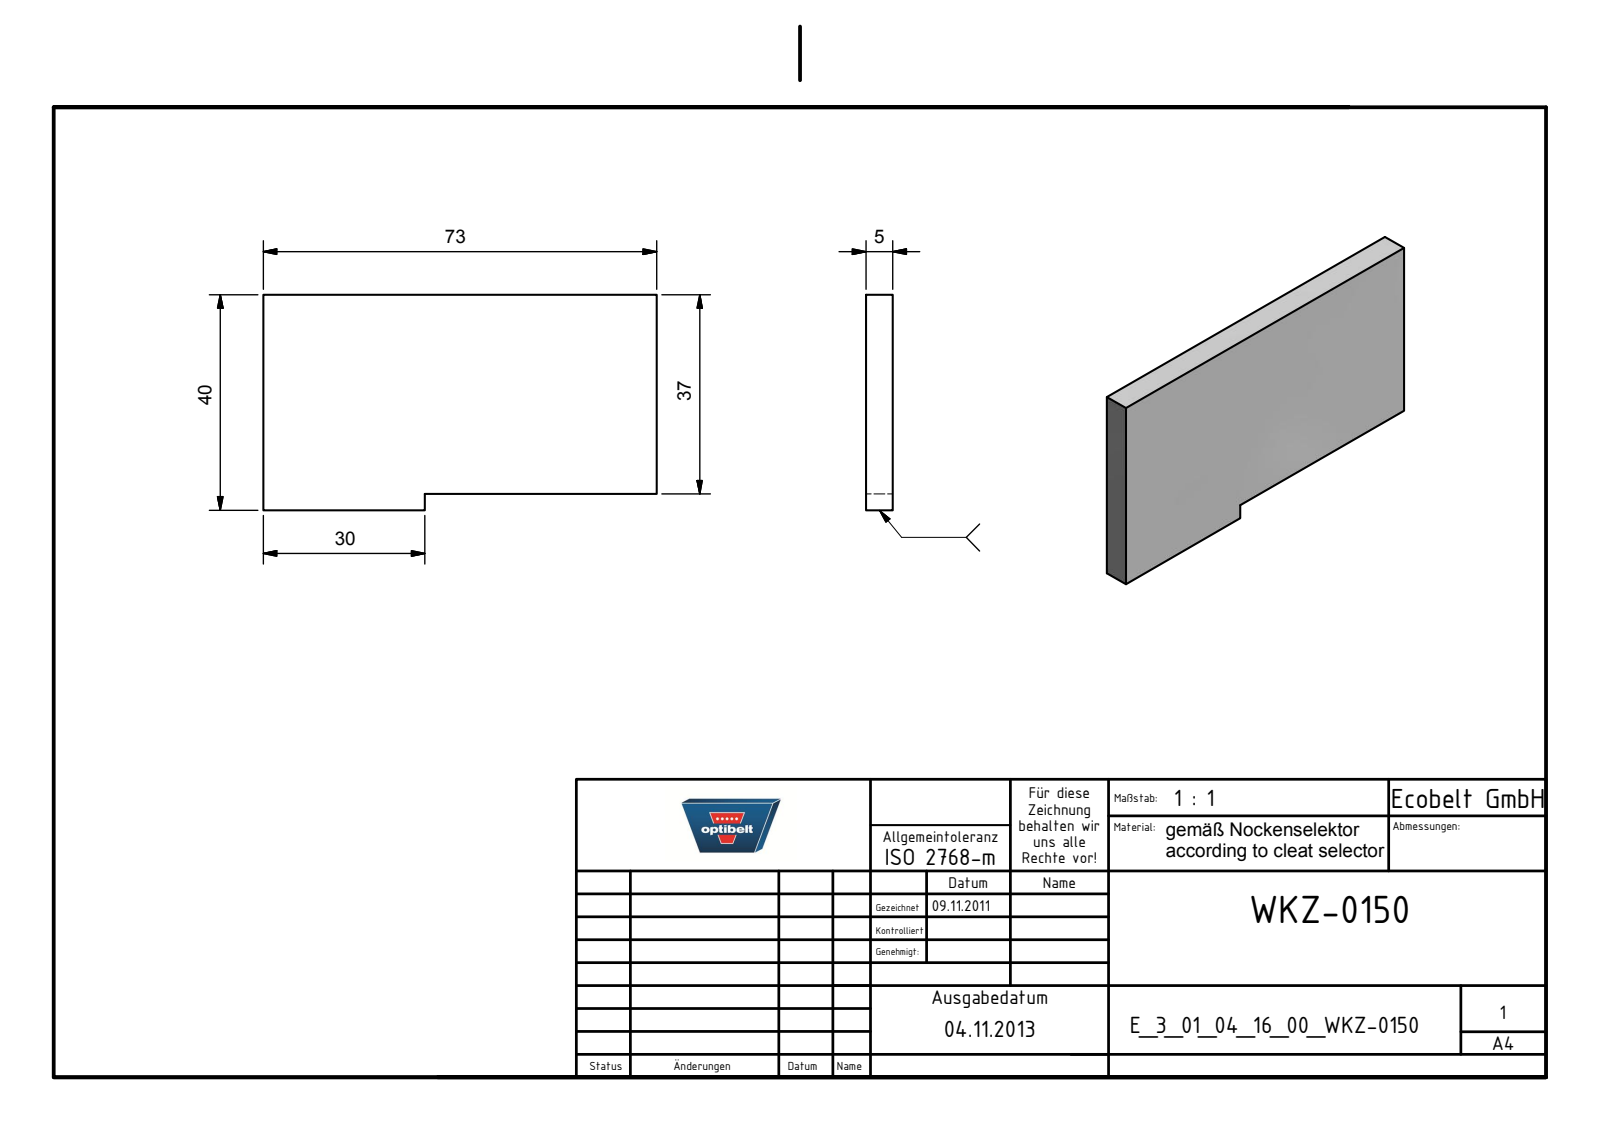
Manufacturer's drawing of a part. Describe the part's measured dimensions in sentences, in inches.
The part is named "E_3_01_04_16_00_WKZ-0150". Its 3-D file was written by "Autodesk Inventor 2025 (AUTOMOTIVE_DESIGN)". It is 1 solid with 8 faces: 8 planar, 0 cylindrical and 0 other. Overall it measures 2.874 by 1.575 by 0.197 inches. Its volume is 0.852 cubic inches and its surface area 10.4 square inches. The main face-to-face distances are 0.197, 1.457, 2.874, 0.118, 1.575, 1.181, 1.693.
